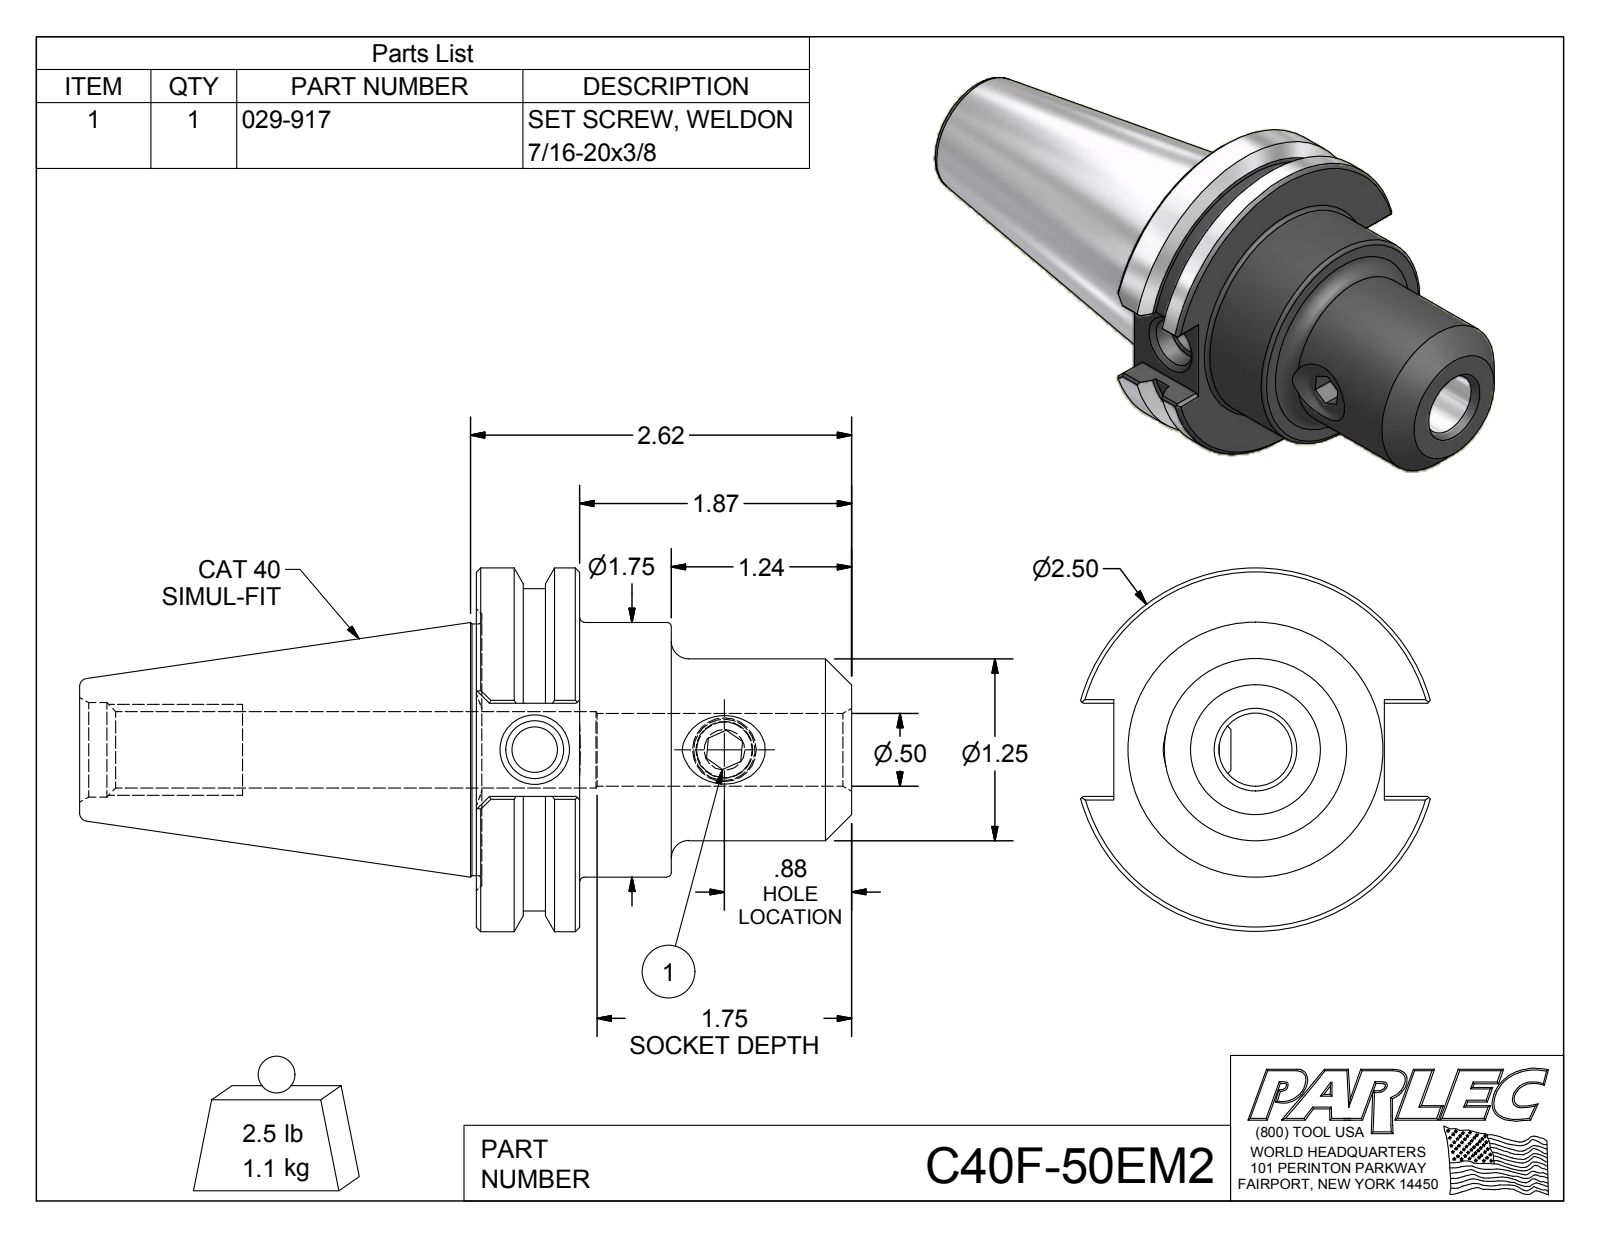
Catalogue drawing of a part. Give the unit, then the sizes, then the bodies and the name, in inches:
Units: inches
Overall size (bounding box): 5.308 × 2.5 × 2.406
Round holes (diameter × count): ⌀0.315 ×1, ⌀0.383 ×1, ⌀0.399 ×1, ⌀0.5 ×1, ⌀0.527 ×1, ⌀0.648 ×1
Round bosses / shafts (diameter × count): ⌀2.5 ×1, ⌀2.215 ×1, ⌀1.75 ×1, ⌀1.73 ×1, ⌀1.25 ×1, ⌀0.437 ×1
Main face-to-face distances: 0.711, 1.341, 0.63, 2.581, 1.87, 1.24, 1.86, 0.236, 0.64, 0.037
Hole centre spacings: 1.305
Volume: 8.895 in³ · Surface area: 43.54 in²
Bodies: 2 solids, 88 faces (42 planar, 16 cylindrical, 30 other)
Part name (STEP PRODUCT): C40F-50EM2; C40F-50EM2-1; 029-917
STEP written by: Autodesk Inventor 2012 (AUTOMOTIVE_DESIGN)
